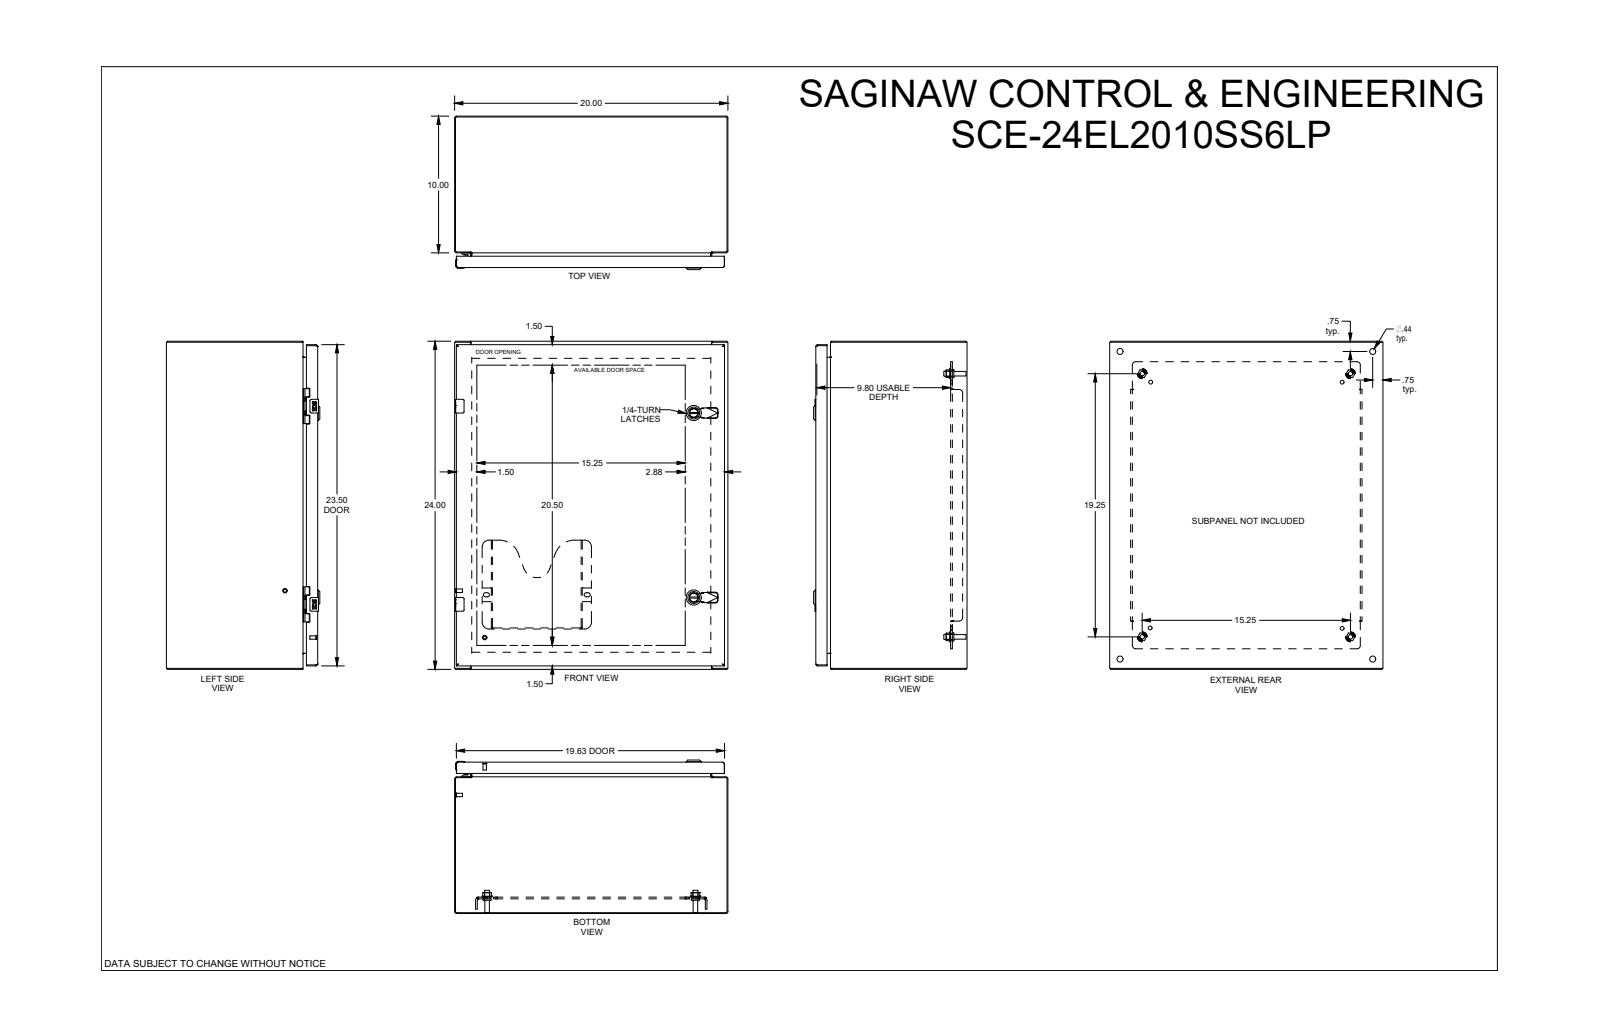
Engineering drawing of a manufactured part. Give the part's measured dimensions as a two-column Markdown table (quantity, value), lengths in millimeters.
| quantity | value |
| --- | --- |
| part name | SCE-24EL2010LP |
| STEP written by | SolidWorks 2021 (AUTOMOTIVE_DESIGN) |
| units | millimeters |
| bodies | 45 solids, 2787 faces (1089 planar, 840 cylindrical, 858 other) |
| overall size | 609.6 × 508 × 285.2 |
| volume | 3 486 000 mm³ |
| surface area | 3 338 000 mm² |
| round holes (diameter × count) | 4.4 × 4, 5.2 × 4, 6.2 × 4, 6.8 × 4, 7.1 × 4, 9.3 × 4, 9.5 × 4, 11.1 × 4, 12.7 × 4, 1 × 2, 4.8 × 2, 5 × 2 |
| round bosses / shafts (diameter × count) | 4.3 × 6, 9.3 × 4, 8.4 × 4, 6.4 × 4, 6.3 × 4, 6.1 × 4, 5 × 3, 28 × 2 |
| partial cylindrical surfaces (radius × count) | 0.3 × 56, 0.3 × 28, 0.4 × 24, 0.5 × 20, 1 × 17, 1.5 × 13, 0.7 × 12, 2.5 × 12 |
| main face-to-face distances | 1.9, 1.5, 506.1, 281.3, 279.3, 279.7, 277.8, 607.7, 25.4, 3.2 |
| hole center spacings | 25, 368.3, 0.5, 12.5, 12.5, 22.2, 58.4, 114.1 |
